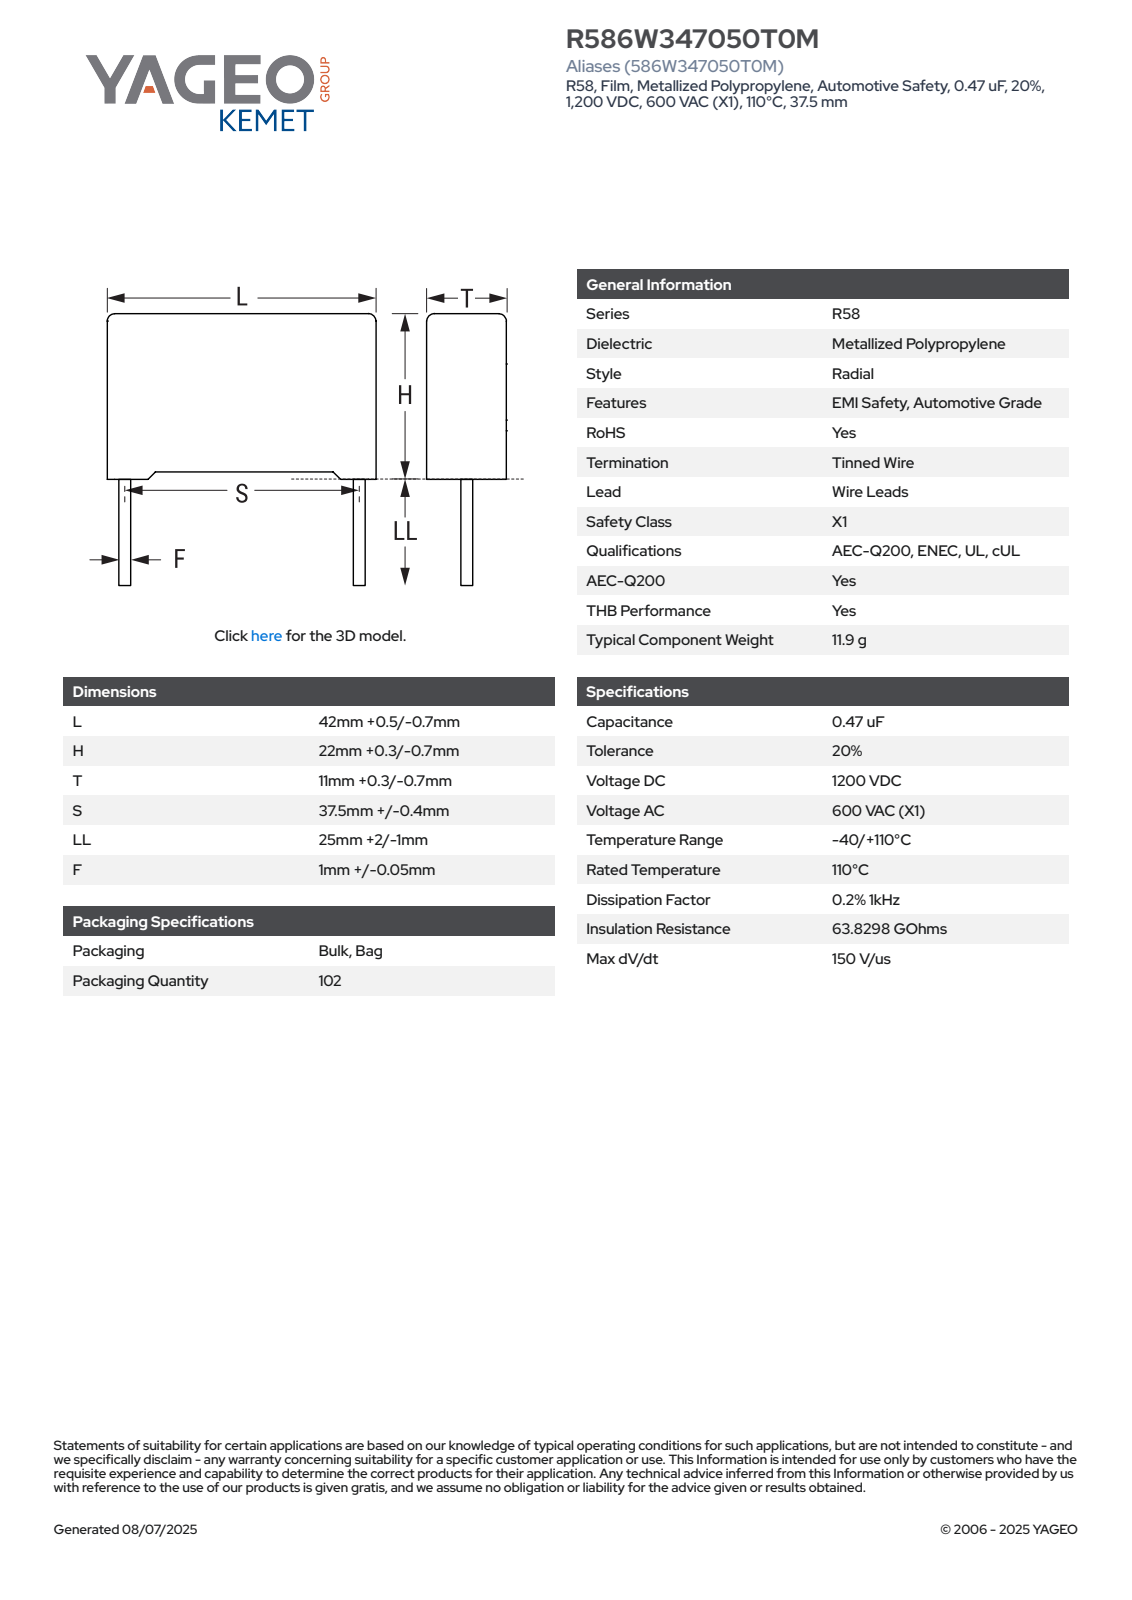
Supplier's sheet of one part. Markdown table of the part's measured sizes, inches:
| quantity | value |
| --- | --- |
| part name | CFR_RB2_42X22X11_L42.5H22.3T11.3S37.5LL27F1.05 |
| STEP written by | SolidWorks 2021 (AUTOMOTIVE_DESIGN) |
| units | inches |
| bodies | 4 solids, 85 faces (77 planar, 8 cylindrical, 0 other) |
| overall size | 1.941 × 1.673 × 0.445 |
| volume | 0.636 in³ |
| surface area | 5.622 in² |
| round bosses / shafts (diameter × count) | 0.041 × 2 |
| partial cylindrical surfaces (radius × count) | 0.02 × 4 |
| main face-to-face distances | 0.445, 0.848, 1.673, 0.848, 0.03, 0.03, 0.878, 0.445, 0.056, 1.617 |
